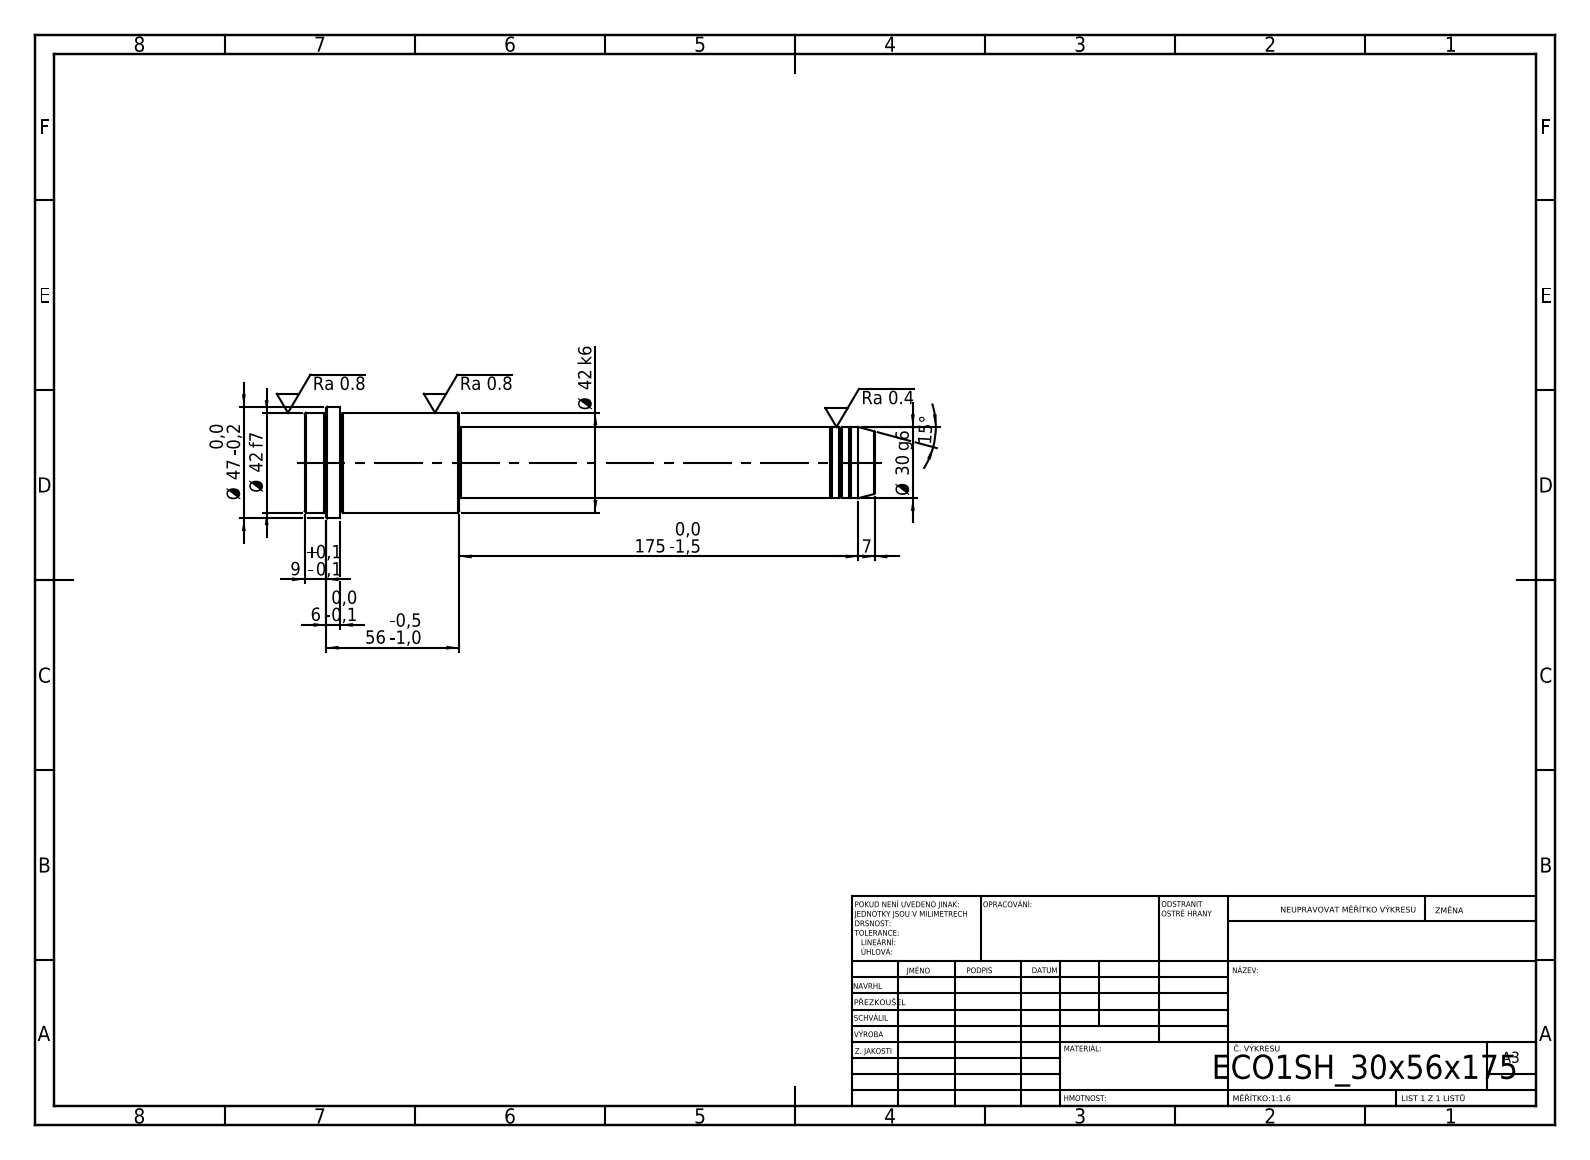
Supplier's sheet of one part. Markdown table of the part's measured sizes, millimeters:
| quantity | value |
| --- | --- |
| STEP written by | SolidWorks 2019 (CONFIG_CONTROL_DESIGN) |
| units | millimeters |
| bodies | 1 solid, 52 faces (6 planar, 16 cylindrical, 30 other) |
| overall size | 240 × 47 × 47 |
| volume | 214 946 mm³ |
| surface area | 28 704 mm² |
| round bosses / shafts (diameter × count) | 47 × 1, 42 × 1, 30 × 1, 29 × 1 |
| main face-to-face distances | 65, 175, 240, 225, 50, 15, 231, 56, 6, 9 |
